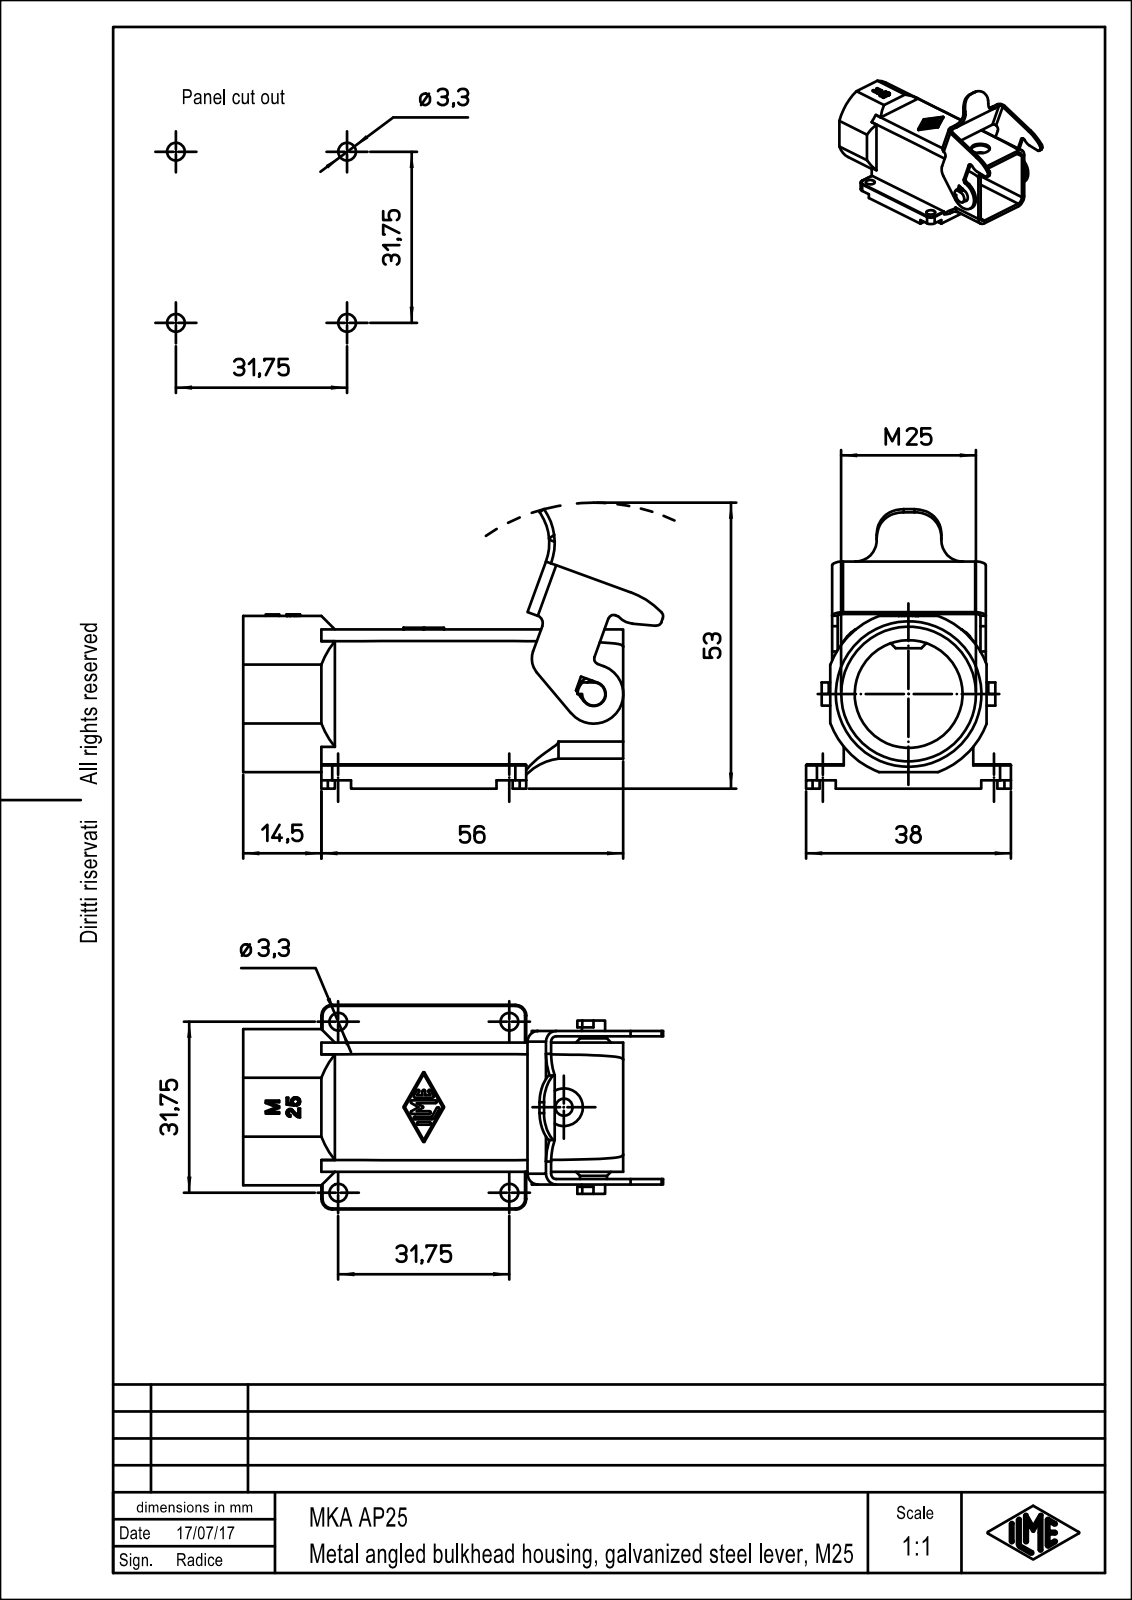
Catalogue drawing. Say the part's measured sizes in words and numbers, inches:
The part is named "MKA_AP25". Its 3-D file was written by "PTC Creo Elements/Direct Modeling 19.0E 27-Jun-2016 (C) Parametric Technology GmbH (AUTOMOTIVE_DESIGN)". It is 1 solid with 387 faces: 258 planar, 108 cylindrical and 21 other. Overall it measures 3.067 by 2.042 by 1.496 inches. Its volume is 0.978 cubic inches and its surface area 28.18 square inches. Round holes: 4 of diameter 0.13, 1 of diameter 0.126, 1 of diameter 0.276, 1 of diameter 0.787, 1 of diameter 0.984. Round bosses or shafts: 1 of diameter 0.197, 1 of diameter 0.169. Partial cylindrical surfaces (rounded edges, fillets, slot ends): 18 of radius 0.079, 15 of radius 0.01, 6 of radius 0.039, 6 of radius 0.126, 4 of radius 0.008, 4 of radius 0.157, 3 of radius 0.005, 2 of radius 0.197. The main face-to-face distances are 0.047, 0.898, 0.945, 0.85, 1.043, 0.039, 0.093, 0.99, 1.083, 0.098. The hole center spacings are 1.25, 1.763, 1.768, 0.741, 0.742.
